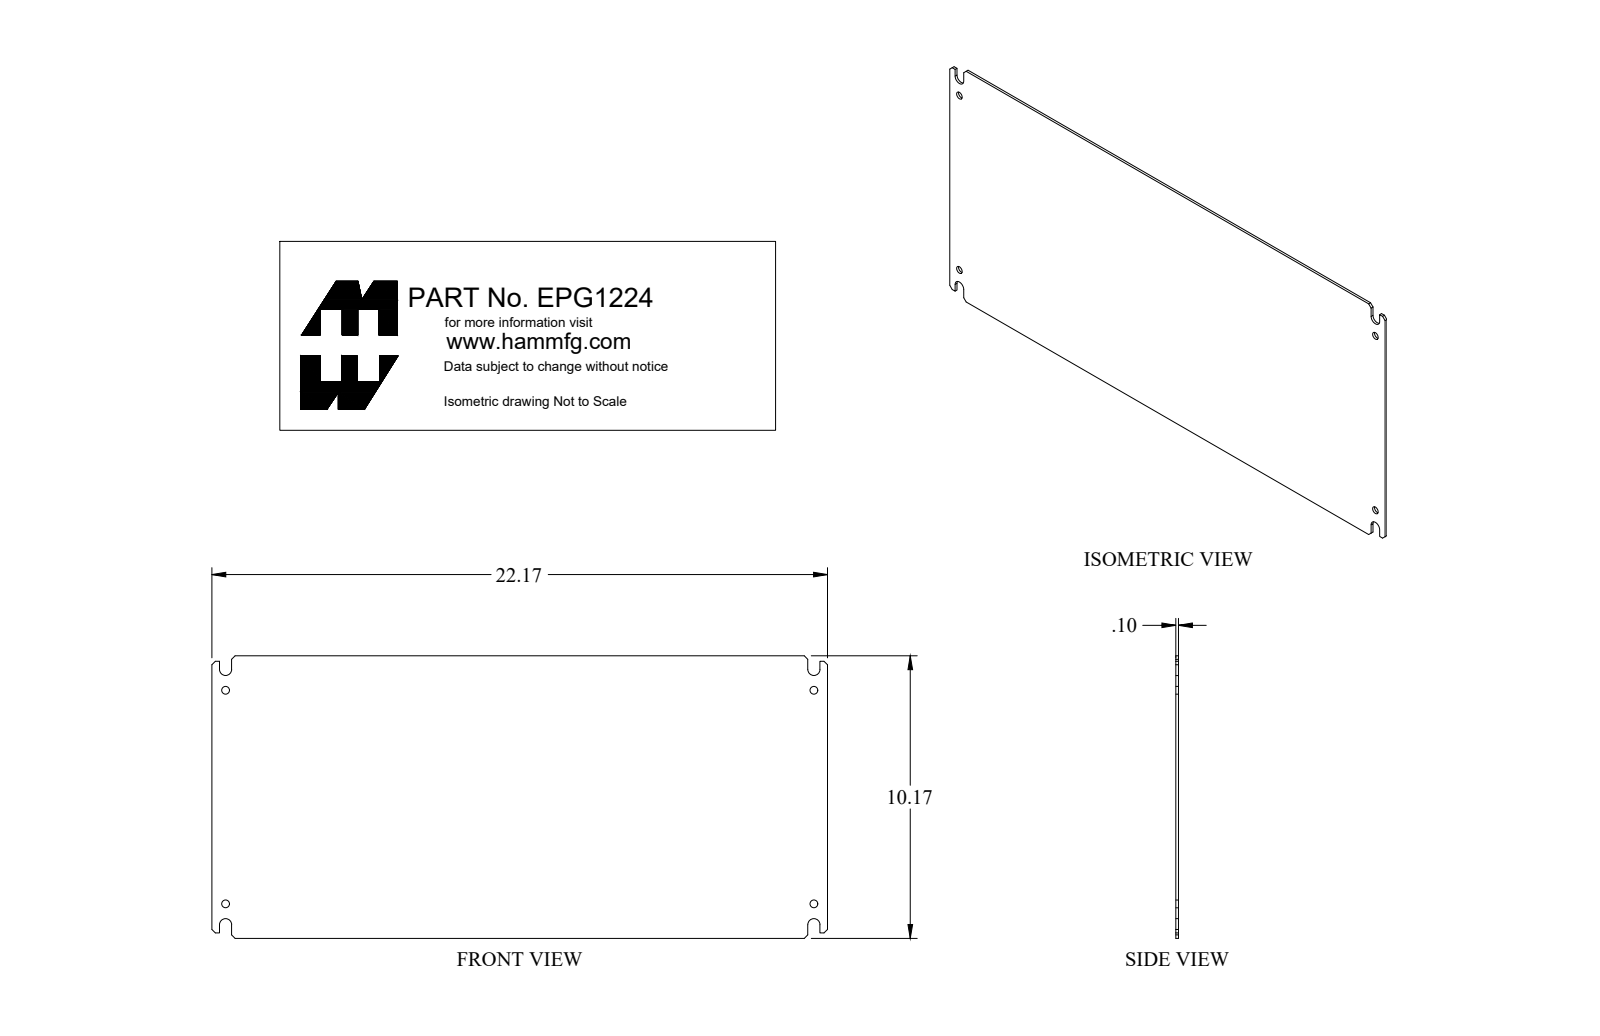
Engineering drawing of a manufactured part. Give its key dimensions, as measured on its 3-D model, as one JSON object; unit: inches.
{"part_name": "EPG1224", "step_written_by": "SolidWorks 2018 (AUTOMOTIVE_DESIGN)", "units": "inches", "bodies": {"solids": 1, "faces": 40, "planar": 26, "cylindrical": 14, "other": 0}, "overall_size": [22.17, 10.17, 0.095], "volume_in3": 21.26, "surface_area_in2": 454.3, "round_holes": [[0.281, 4]], "partial_cylinders_radius": [[0.219, 4]], "face_to_face_distances": [0.095, 10.17, 22.17, 0.709, 21.461, 0.272, 21.898, 0.437, 21.188, 20.751], "hole_center_spacings": [7.688, 21.188, 22.54]}
